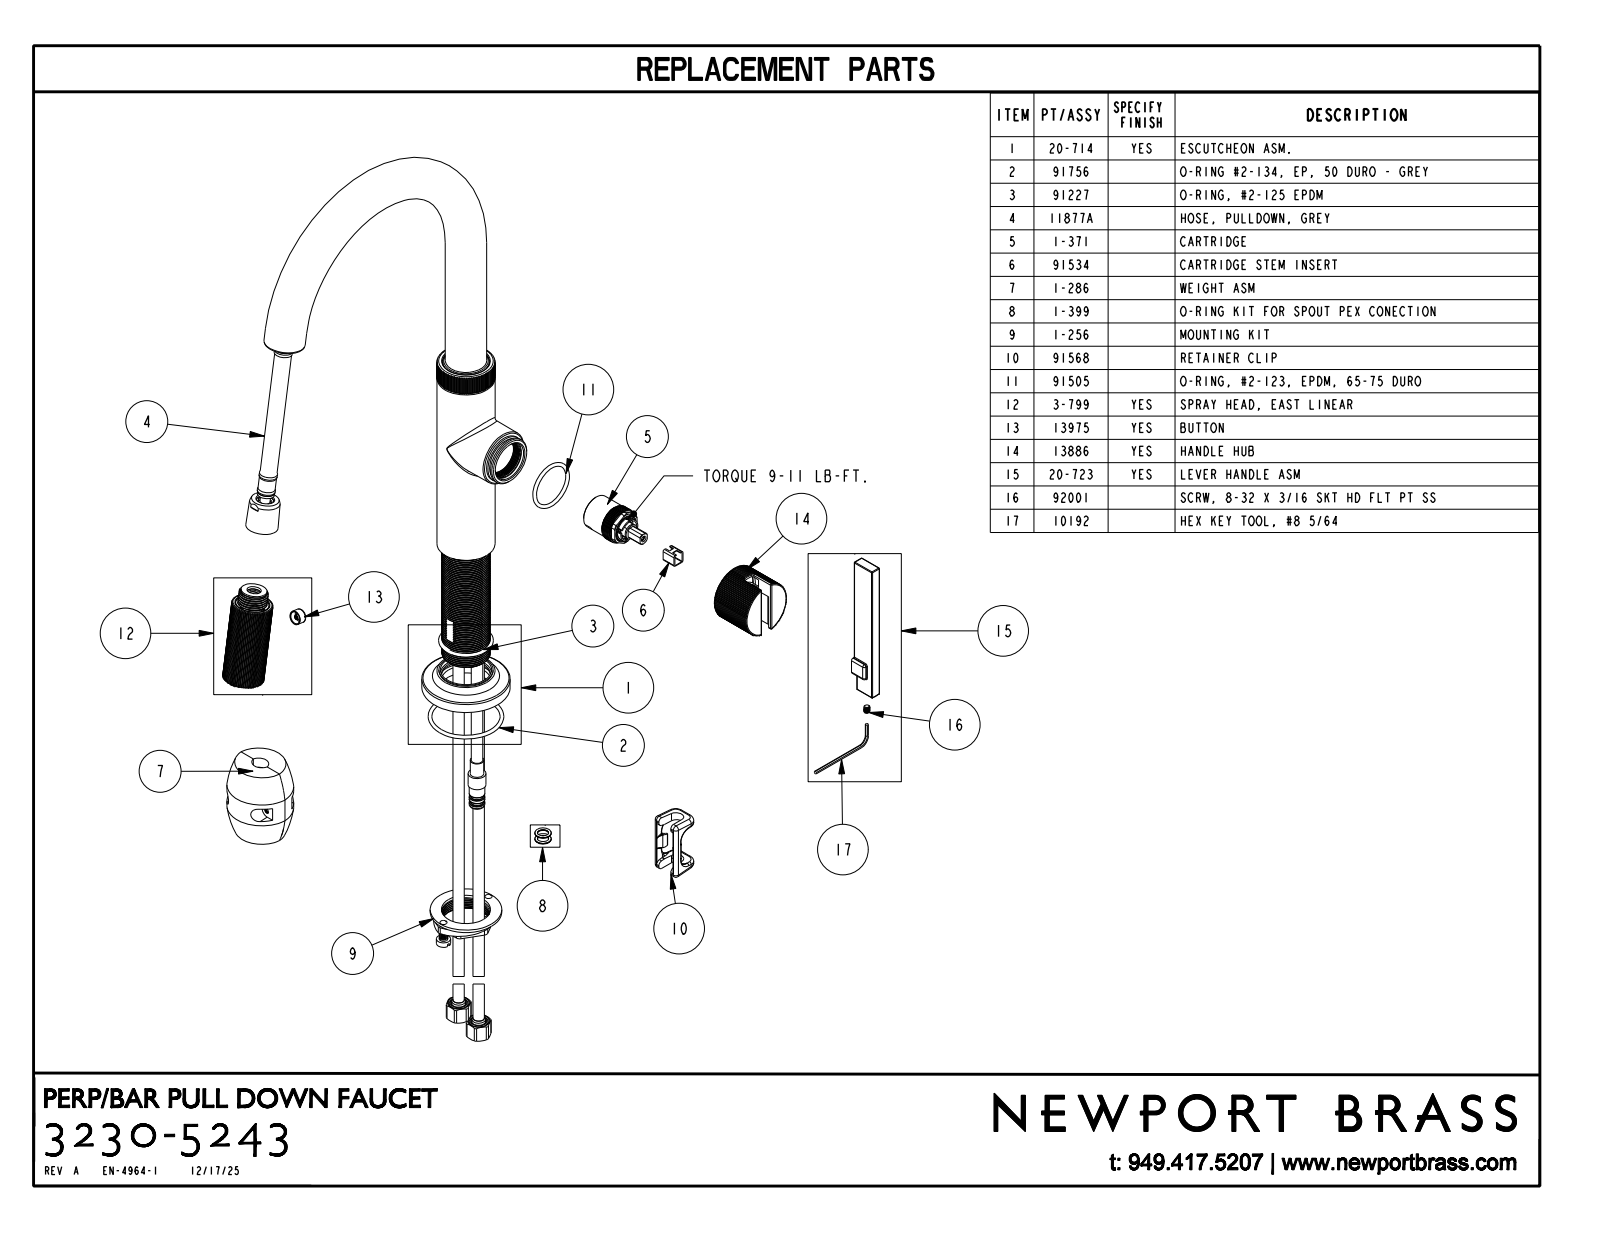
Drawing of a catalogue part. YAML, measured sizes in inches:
part_name: "13872; 20-714_ASM; 13994; 13672 (+8 more)"
step_written_by: "CREO PARAMETRIC BY PTC INC, 2023134 (CONFIG_CONTROL_DESIGN)"
units: inches
bodies: {solids: 19, faces: 2725, planar: 1597, cylindrical: 834, other: 294}
overall_size: [14.773, 9.191, 3.972]
volume: 37.65
surface_area: 197.6
round_holes:
  - {diameter: 0.039, count: 48}
  - {diameter: 0.598, count: 2}
  - {diameter: 0.638, count: 2}
  - {diameter: 0.135, count: 1}
  - {diameter: 0.236, count: 1}
  - {diameter: 0.394, count: 1}
  - {diameter: 0.472, count: 1}
  - {diameter: 0.52, count: 1}
  - {diameter: 0.559, count: 1}
  - {diameter: 0.591, count: 1}
  - {diameter: 0.82, count: 1}
  - {diameter: 0.827, count: 1}
round_bosses_or_shafts:
  - {diameter: 0.102, count: 18}
  - {diameter: 0.079, count: 18}
  - {diameter: 0.551, count: 2}
  - {diameter: 2.43, count: 1}
  - {diameter: 1.6, count: 1}
  - {diameter: 1.49, count: 1}
  - {diameter: 1.451, count: 1}
  - {diameter: 1.354, count: 1}
partial_cylinders:
  - {radius: 0.02, count: 52}
  - {radius: 0.008, count: 21}
  - {radius: 0.02, count: 19}
  - {radius: 0.039, count: 16}
  - {radius: 0.012, count: 8}
  - {radius: 0.06, count: 8}
  - {radius: 0.125, count: 6}
  - {radius: 0.01, count: 4}
face_to_face_distances: [0.015, 0.3, 0.713, 0.315, 6.15, 0.55, 0.59, 0.58, 5.57, 5.56]
hole_center_spacings: [0.364, 0.364, 0.365, 0.225, 0.665, 0.076, 0.487, 0.152]
